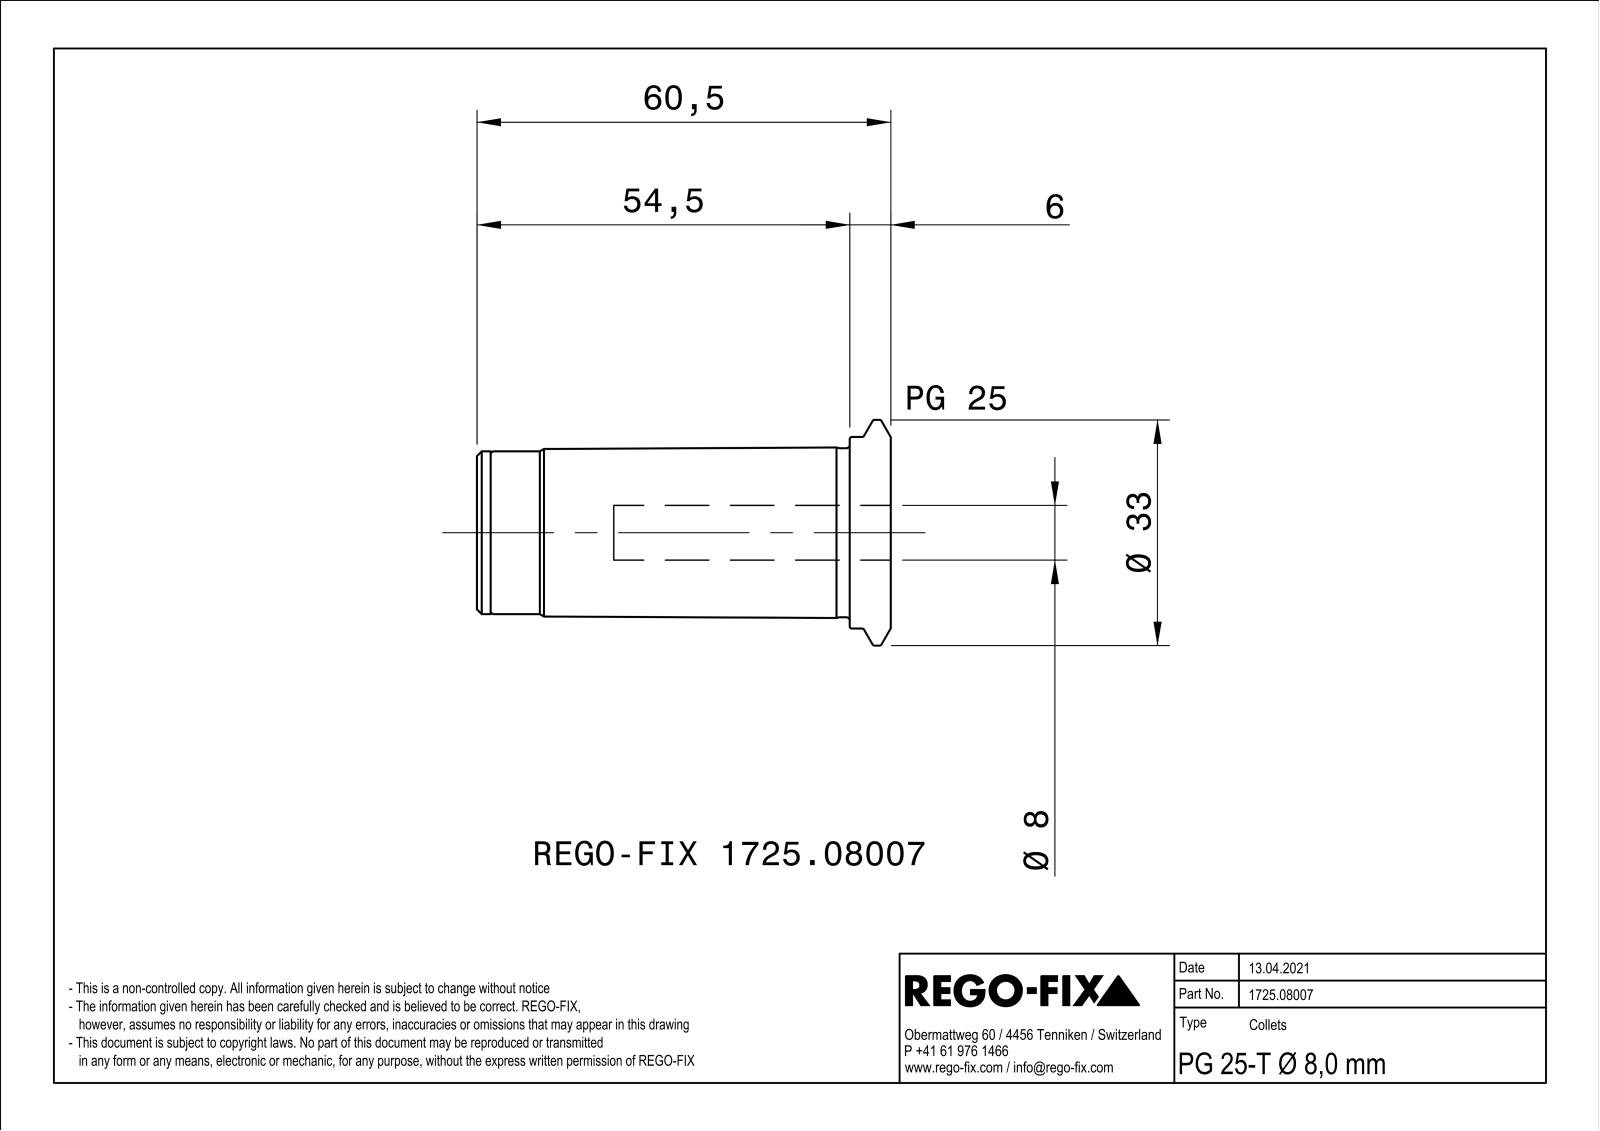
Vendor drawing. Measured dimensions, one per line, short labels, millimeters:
name: NOCUT
written by: SIEMENS PLM Software Solid Edge ST10 (AUTOMOTIVE_DESIGN)
unit: mm
bodies: 0 solids, 88 faces (24 planar, 23 cylindrical, 41 other)
size: 58.5 × 33 × 32.94
holes: 1× ⌀3.24, 1× ⌀4.3, 1× ⌀8, 1× ⌀9, 1× ⌀21, 1× ⌀22
bosses: 1× ⌀33, 1× ⌀28, 1× ⌀24.7, 1× ⌀23.8
rounds: 2× R0.5, 1× R4.06, 1× R4.17
face distances: 1, 6, 55.9, 57, 49.9, 51, 1.1, 58.5, 52.5, 2.6
